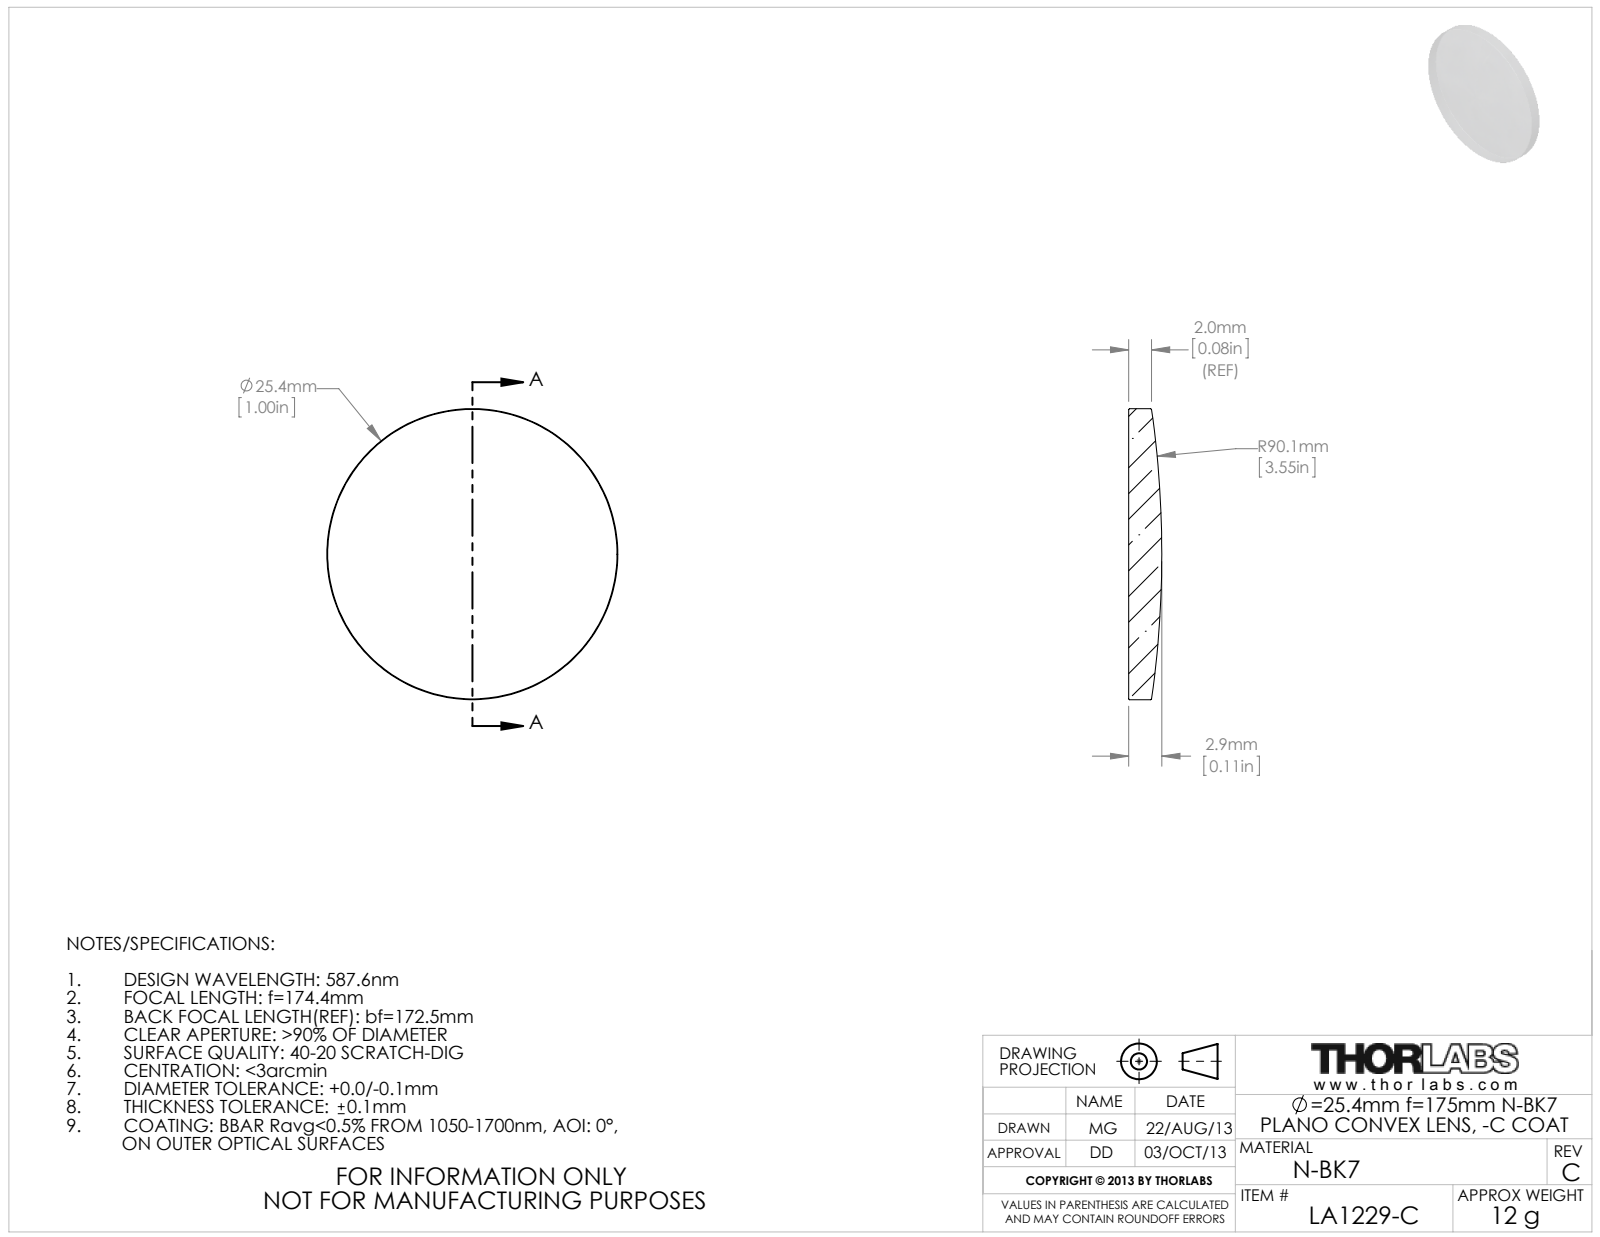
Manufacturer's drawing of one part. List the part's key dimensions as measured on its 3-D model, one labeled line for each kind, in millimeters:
Part name (STEP PRODUCT): 4587-E0W
STEP written by: SolidWorks 2009 (AUTOMOTIVE_DESIGN)
Units: millimetres
Bodies: 1 solid, 5 faces (1 planar, 2 cylindrical, 2 other)
Overall size (bounding box): 25.4 × 25.4 × 2.89
Volume: 1 237 mm³ · Surface area: 1 175 mm²
Round bosses / shafts (diameter × count): ⌀25.4 ×1
